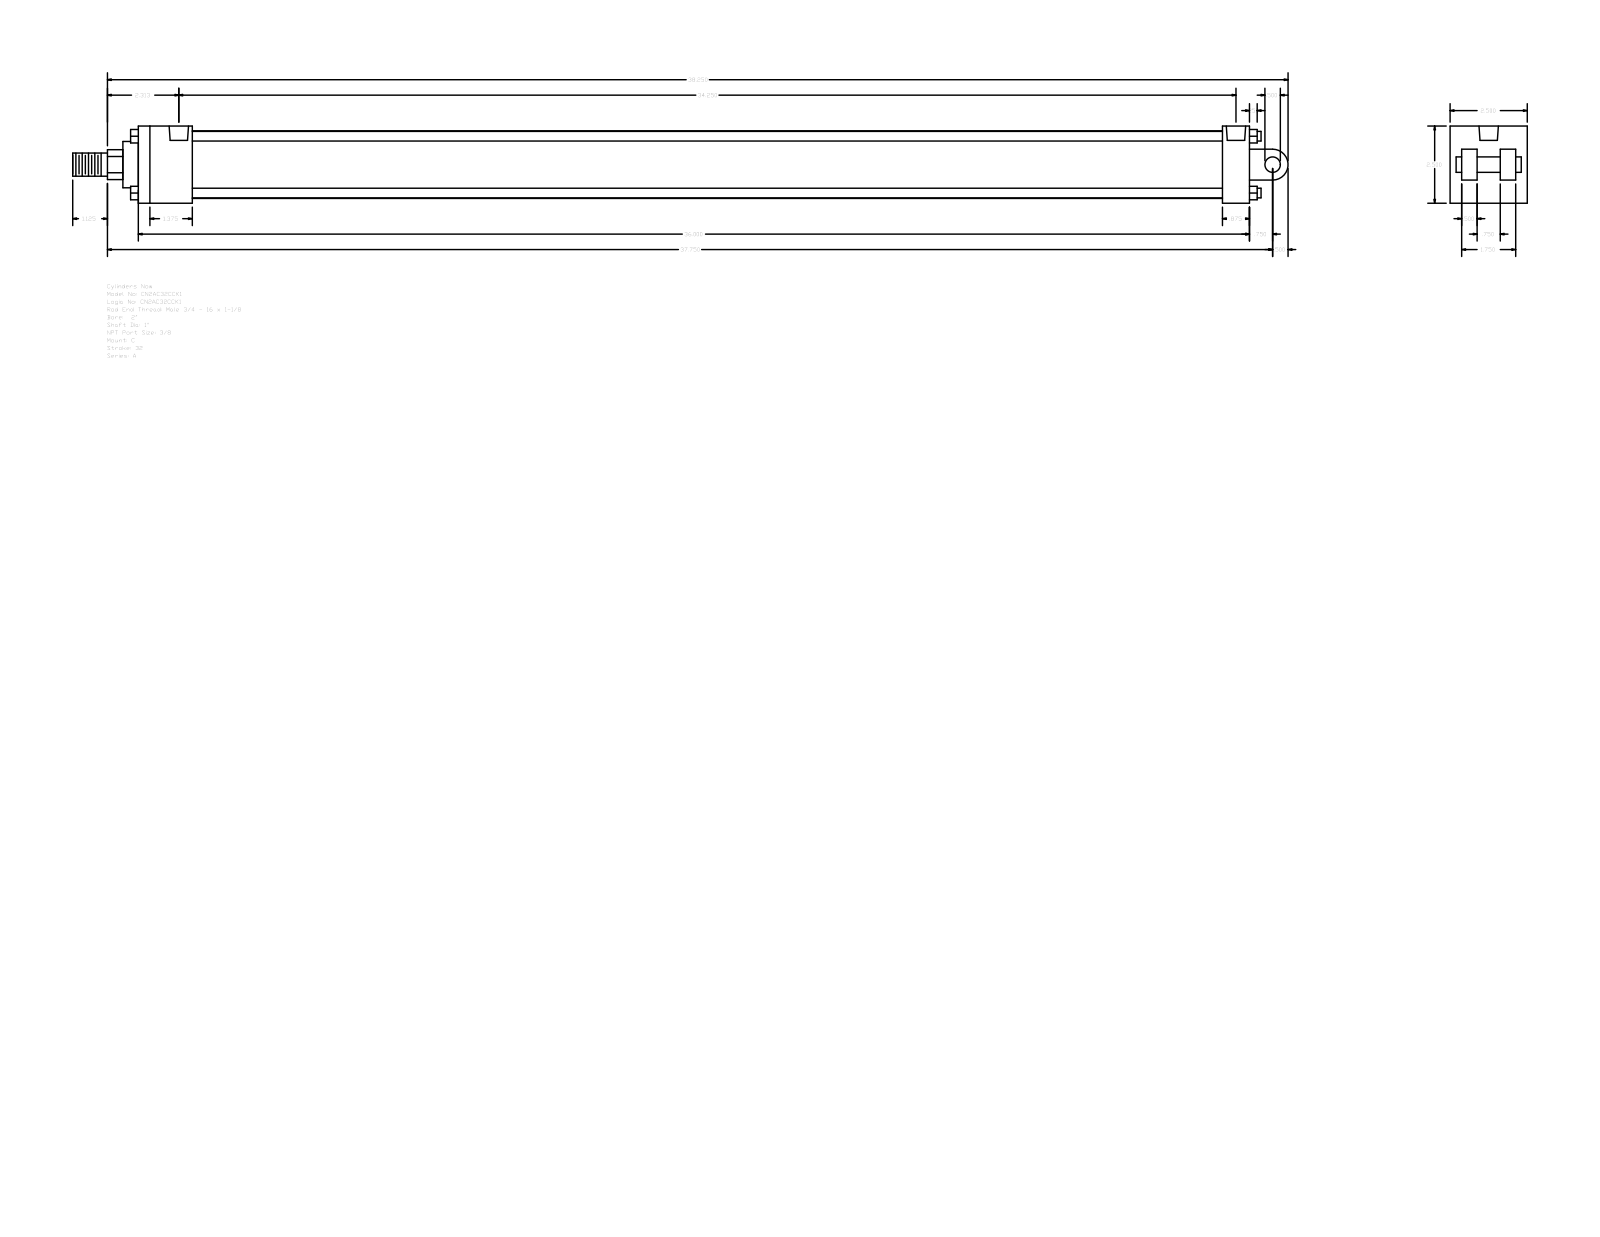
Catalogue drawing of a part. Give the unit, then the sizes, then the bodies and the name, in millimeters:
Units: millimetres
Overall size (bounding box): 1000.12 × 63.5 × 63.5
Round holes (diameter × count): ⌀5.56 ×4, ⌀15.93 ×2
Round bosses / shafts (diameter × count): ⌀7.94 ×4, ⌀55.63 ×1, ⌀38.1 ×1, ⌀25.4 ×1, ⌀19.05 ×1, ⌀12.7 ×1
Partial cylindrical surfaces — rounded edges, fillets, slot ends (radius × count): R12.29 ×1, R12.7 ×1
Main face-to-face distances: 63.5, 22.22, 914.4, 44.45, 12.7, 869.95, 892.18, 847.73, 9.52, 53.98
Hole centre spacings: 864.38, 1.59, 3.98, 865.97, 868.36, 869.95
Bodies: 0 solids, 135 faces (102 planar, 33 cylindrical, 0 other)
Part name (STEP PRODUCT): A_C__0200_1
STEP written by: GSSL Pune (CONFIG_CONTROL_DESIGN)
